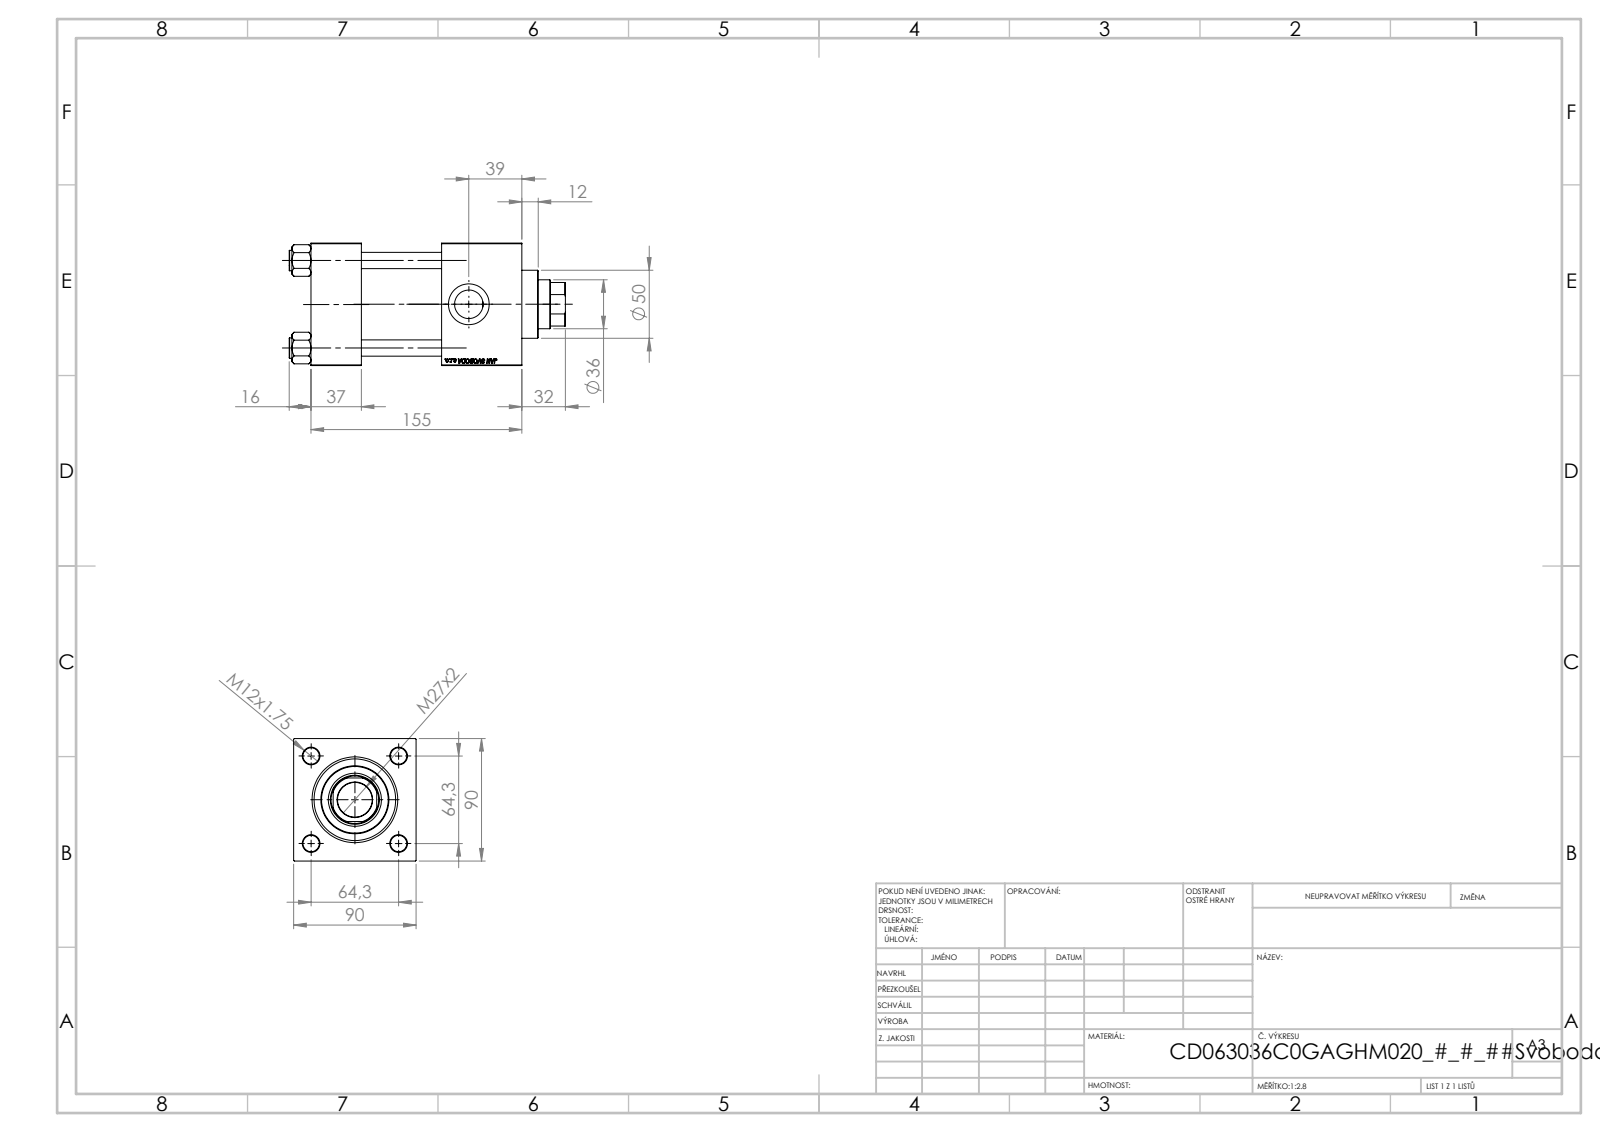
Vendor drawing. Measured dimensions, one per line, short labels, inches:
name: V215CD_Body_C; V215CD_VC_C; NUT_M5_V215CD_C; V215CD_C_TYCINKA (+1 more)
written by: SolidWorks 2019 (CONFIG_CONTROL_DESIGN)
unit: in
bodies: 11 solids, 1149 faces (526 planar, 87 cylindrical, 536 other)
size: 7.992 × 3.543 × 3.543
volume: 59.06 in³; area: 285.6 in²
holes: 4× ⌀0.472, 2× ⌀0.276, 2× ⌀0.825, 2× ⌀1.181, 1× ⌀1.004, 1× ⌀1.417, 1× ⌀1.535, 1× ⌀1.969, 1× ⌀2.362, 1× ⌀2.48
bosses: 4× ⌀0.591, 1× ⌀2.717
rounds: 1× R0.689
face distances: 3.543, 2.323, 1.457, 6.102, 4.646, 3.78, 4.972, 3.516, 1.193, 1.13
hole spacings: 1.79, 2.531, 3.58
